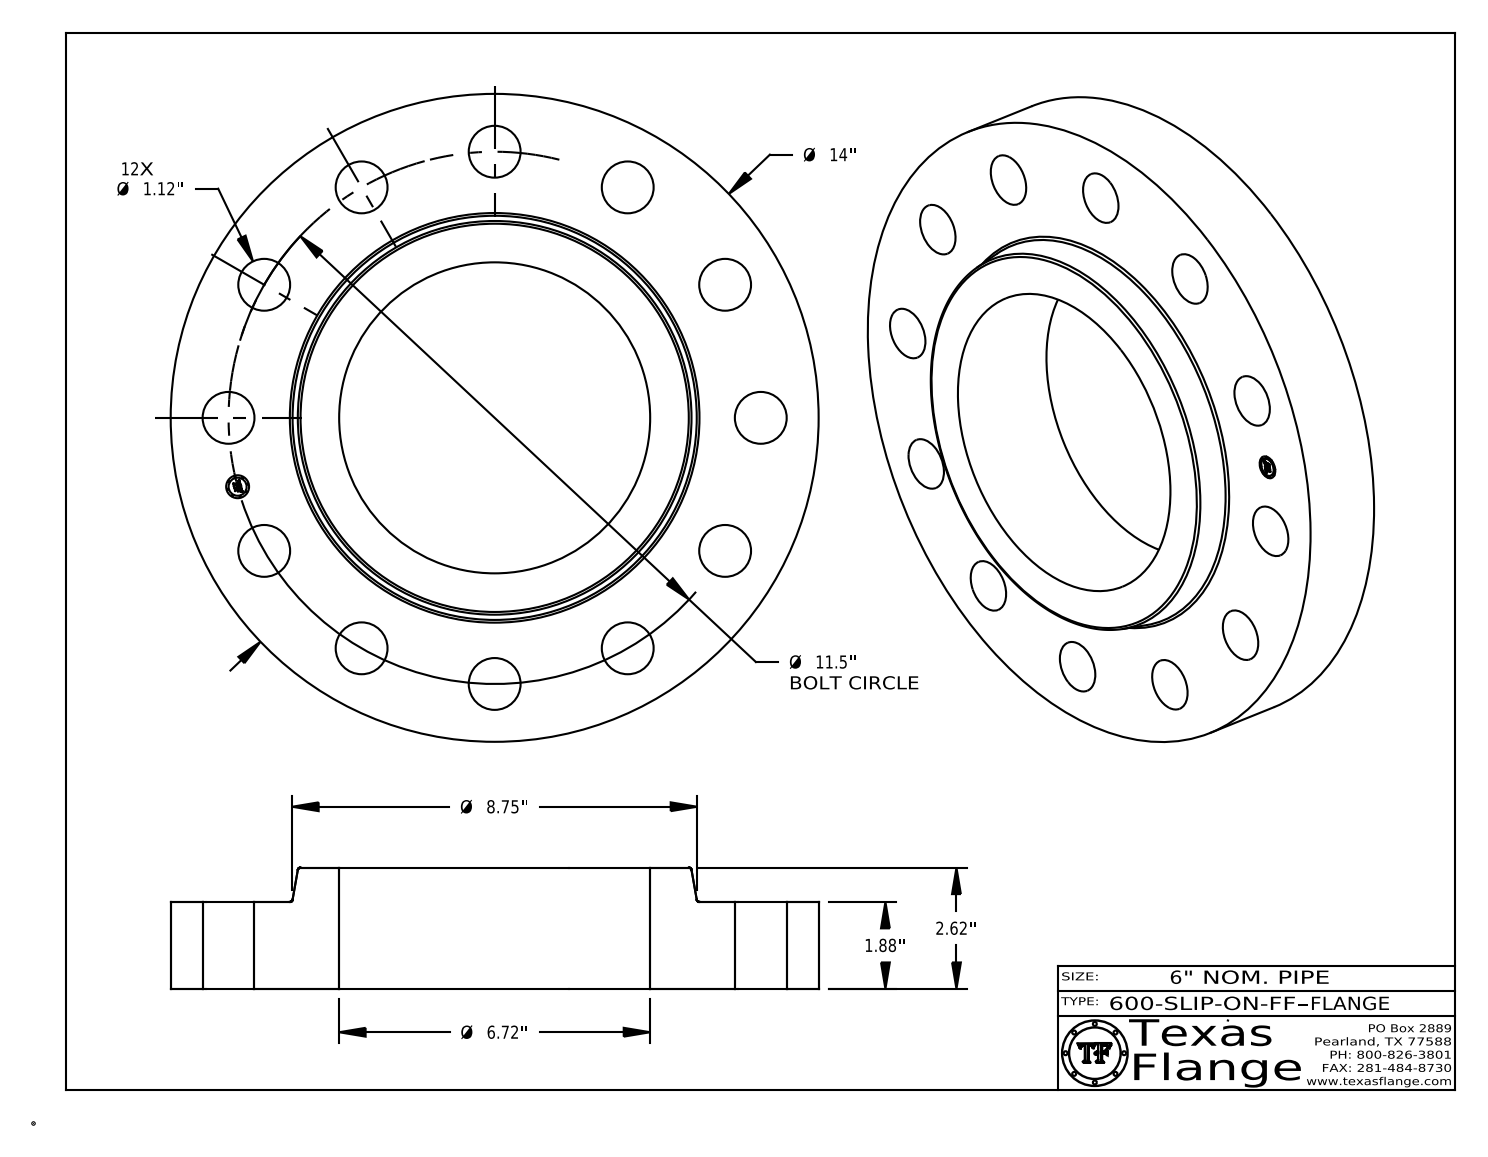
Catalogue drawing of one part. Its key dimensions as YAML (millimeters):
part_name: "600-SLIP-ON-FF"
step_written_by: "CATIA V5 STEP AP214 (AUTOMOTIVE_DESIGN)"
units: millimeters
bodies: {solids: 1, faces: 422, planar: 368, cylindrical: 48, other: 6}
overall_size: [355.6, 355.6, 66.5]
volume: 3563000
surface_area: 288200
round_holes:
  - {diameter: 28.4, count: 12}
  - {diameter: 12.6, count: 1}
  - {diameter: 170.7, count: 1}
round_bosses_or_shafts:
  - {diameter: 0.8, count: 8}
  - {diameter: 355.6, count: 1}
  - {diameter: 9.9, count: 1}
face_to_face_distances: [47.8, 66.5, 18.8, 47.4, 0.4, 19.2, 3.8, 3.7, 0.7, 2.4]
hole_center_spacings: [146.1, 206.6, 282.1, 75.6, 146.1, 253, 292.1, 75.6]
